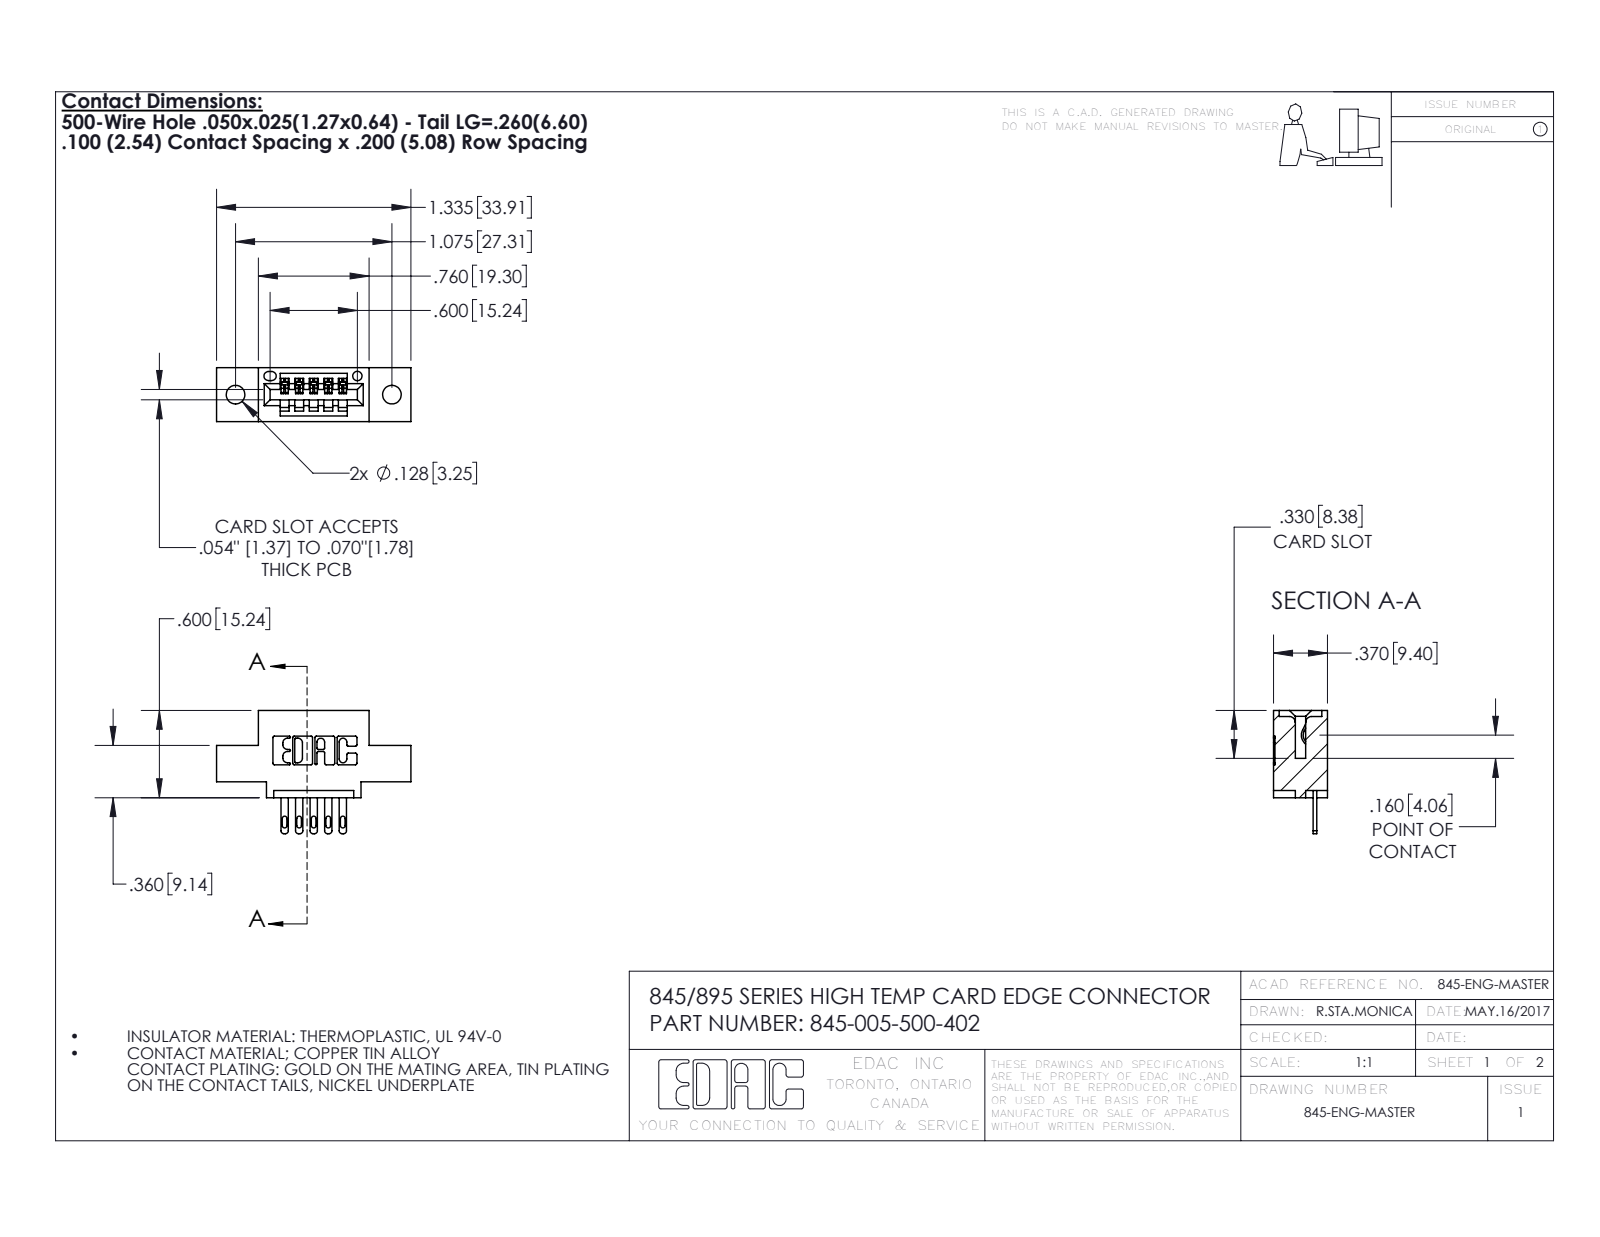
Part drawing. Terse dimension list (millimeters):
name: 345-292-001_345-293-100; 345 Part_0.110 Offset - 0.128 Dia; 345-005-500-402
written by: SolidWorks 2016 (CONFIG_CONTROL_DESIGN)
unit: mm
bodies: 6 solids, 400 faces (254 planar, 146 cylindrical, 0 other)
size: 33.9 × 21.5 × 9.4
volume: 2 820 mm³; area: 3 054 mm²
holes: 2× ⌀3.3, 1× ⌀1.6
rounds: 22× R0.3, 10× R0.2, 10× R0.4, 10× R0.5, 6× R0.2, 6× R0.8, 3× R0.7, 2× R0.8
face distances: 5.1, 9.4, 1.8, 7.6, 2.5, 0.6, 6.4, 2.5, 6.9, 1.5
hole spacings: 6.9, 21.5, 27.3
